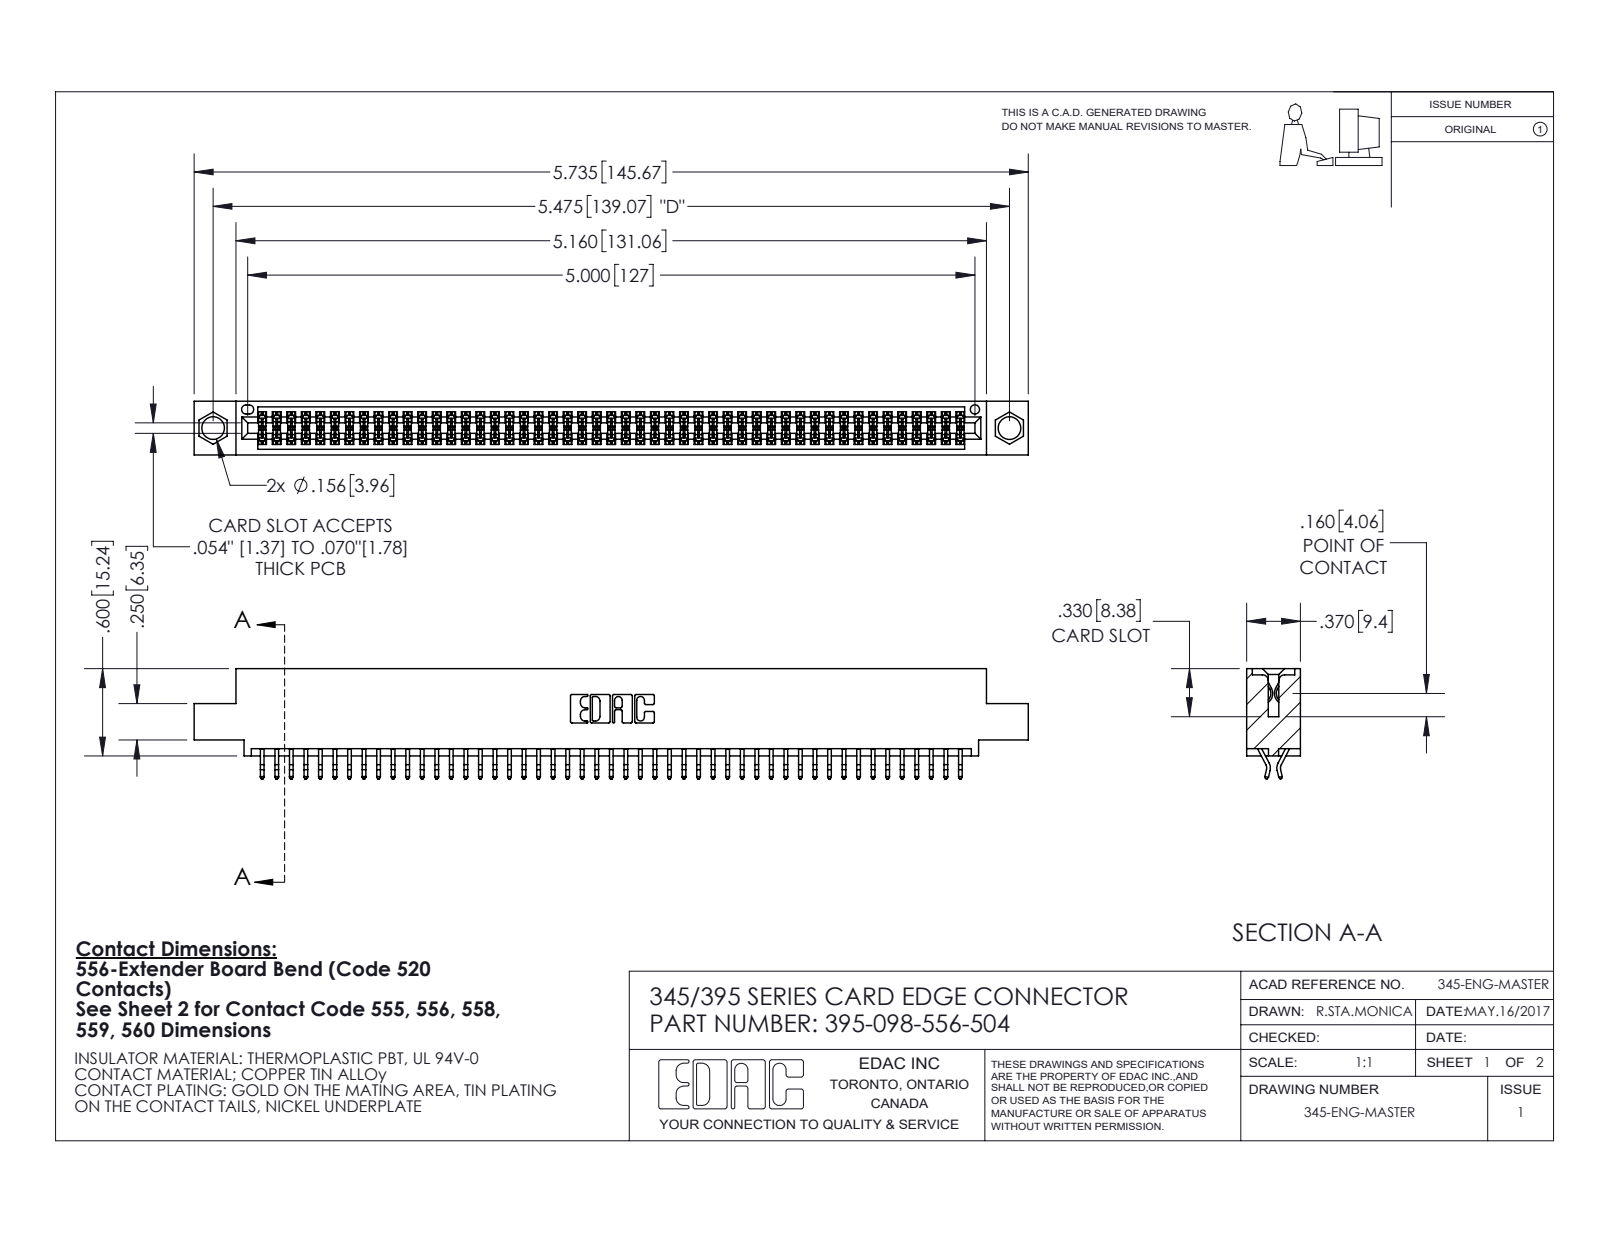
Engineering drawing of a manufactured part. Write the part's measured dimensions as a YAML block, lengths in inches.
part_name: "345-292-001_556 Tail; 345 Part_0.110 Offset - 0.156 Dia-TI; 395-098-556-504"
step_written_by: "SolidWorks 2020 (CONFIG_CONTROL_DESIGN)"
units: inches
bodies: {solids: 99, faces: 5632, planar: 3724, cylindrical: 1908, other: 0}
overall_size: [5.735, 0.757, 0.37]
volume: 0.856
surface_area: 32.14
round_holes:
  - {diameter: 0.156, count: 2}
  - {diameter: 0.064, count: 1}
partial_cylinders:
  - {radius: 0.006, count: 196}
  - {radius: 0.01, count: 22}
  - {radius: 0.007, count: 6}
  - {radius: 0.031, count: 6}
  - {radius: 0.026, count: 3}
  - {radius: 0.01, count: 2}
  - {radius: 0.014, count: 2}
  - {radius: 0.019, count: 2}
face_to_face_distances: [0.298, 0.072, 0.37, 0.2, 0.025, 0.098, 0.272, 0.225, 0.175, 0.149]
hole_center_spacings: [0.27, 5.239, 5.475]
